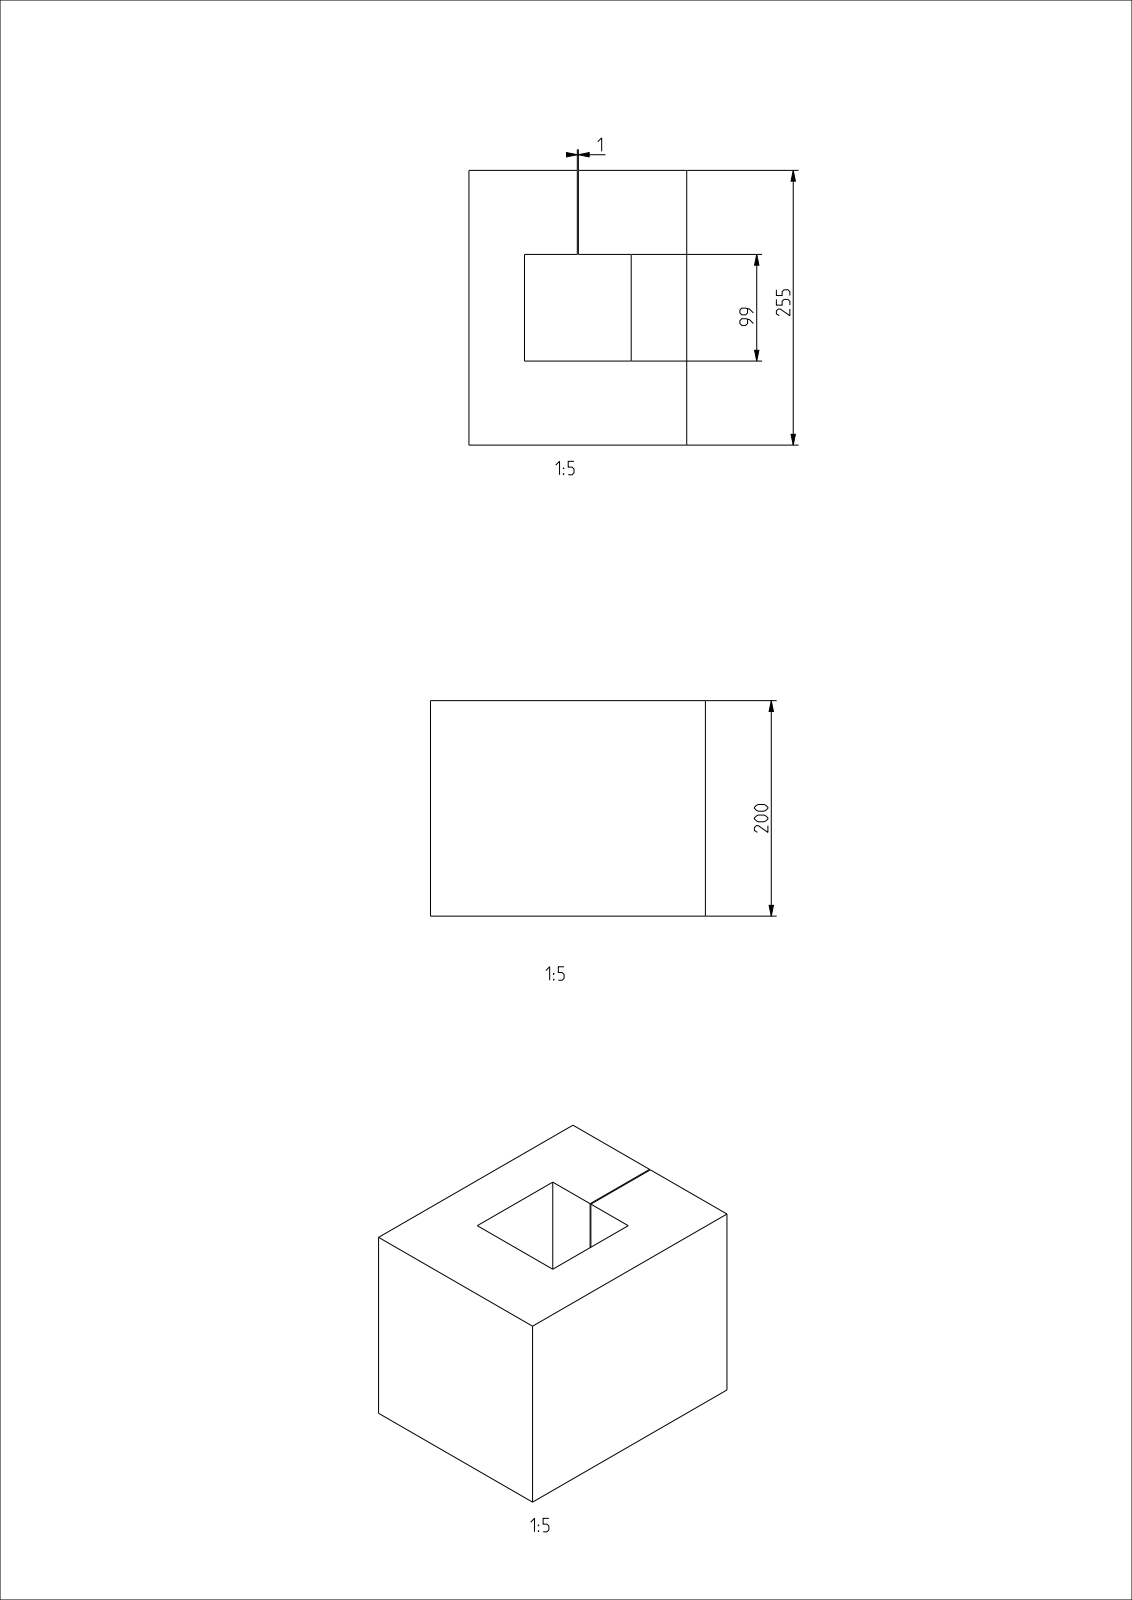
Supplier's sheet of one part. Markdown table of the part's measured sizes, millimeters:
| quantity | value |
| --- | --- |
| part name | 47674-M |
| STEP written by | CREO PARAMETRIC BY PTC INC, 2022281 (AUTOMOTIVE_DESIGN) |
| units | millimeters |
| bodies | 1 solid, 14 faces (14 planar, 0 cylindrical, 0 other) |
| overall size | 255 × 202 × 200 |
| volume | 8 326 000 mm³ |
| surface area | 376 062 mm² |
| main face-to-face distances | 202, 200, 255, 51.5, 150.5, 99, 78, 177, 100.5, 101.5 |
